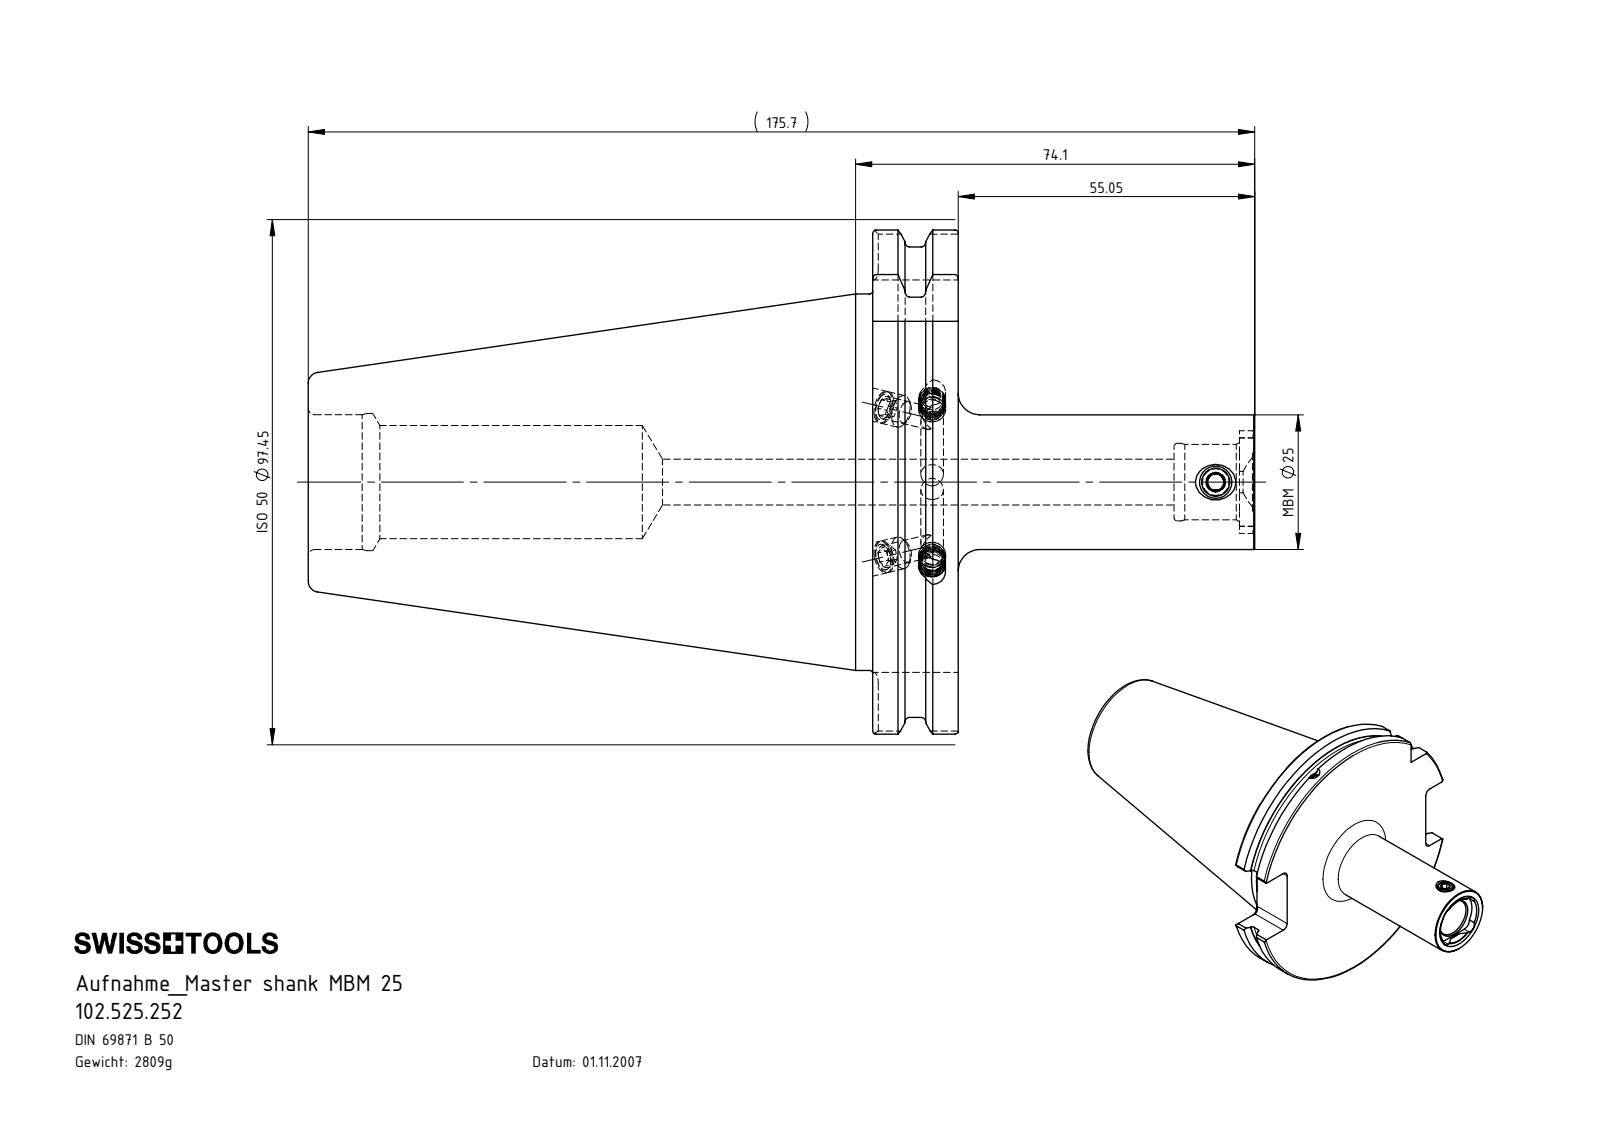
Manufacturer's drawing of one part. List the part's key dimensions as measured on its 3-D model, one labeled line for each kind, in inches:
Part name (STEP PRODUCT): ISO 4026 - M6 x 5_PreviewCfg; KVT_MB_600_050; 102.525.252; MB2-ER1.001.008_A (+1 more)
STEP written by: SolidWorks 2017 (CONFIG_CONTROL_DESIGN)
Units: inches
Bodies: 8 solids, 297 faces (77 planar, 82 cylindrical, 138 other)
Overall size (bounding box): 6.917 × 3.837 × 3.681
Volume: 21.85 in³ · Surface area: 76.49 in²
Round holes (diameter × count): ⌀0.165 ×3, ⌀0.157 ×2, ⌀0.236 ×2, ⌀0.118 ×1, ⌀0.197 ×1, ⌀0.207 ×1, ⌀0.335 ×1, ⌀0.551 ×1, ⌀0.567 ×1, ⌀0.827 ×1, ⌀0.984 ×1, ⌀1.002 ×1
Round bosses / shafts (diameter × count): ⌀3.583 ×1, ⌀2.75 ×1, ⌀0.236 ×1, ⌀0.197 ×1
Partial cylindrical surfaces — rounded edges, fillets, slot ends (radius × count): R0.079 ×8, R0.106 ×4, R0.315 ×1, R0.375 ×1, R1.919 ×1
Main face-to-face distances: 0.624, 4.126, 4.75, 2.866, 1.012, 6.917, 2.791, 2.167, 1.681, 0.669
